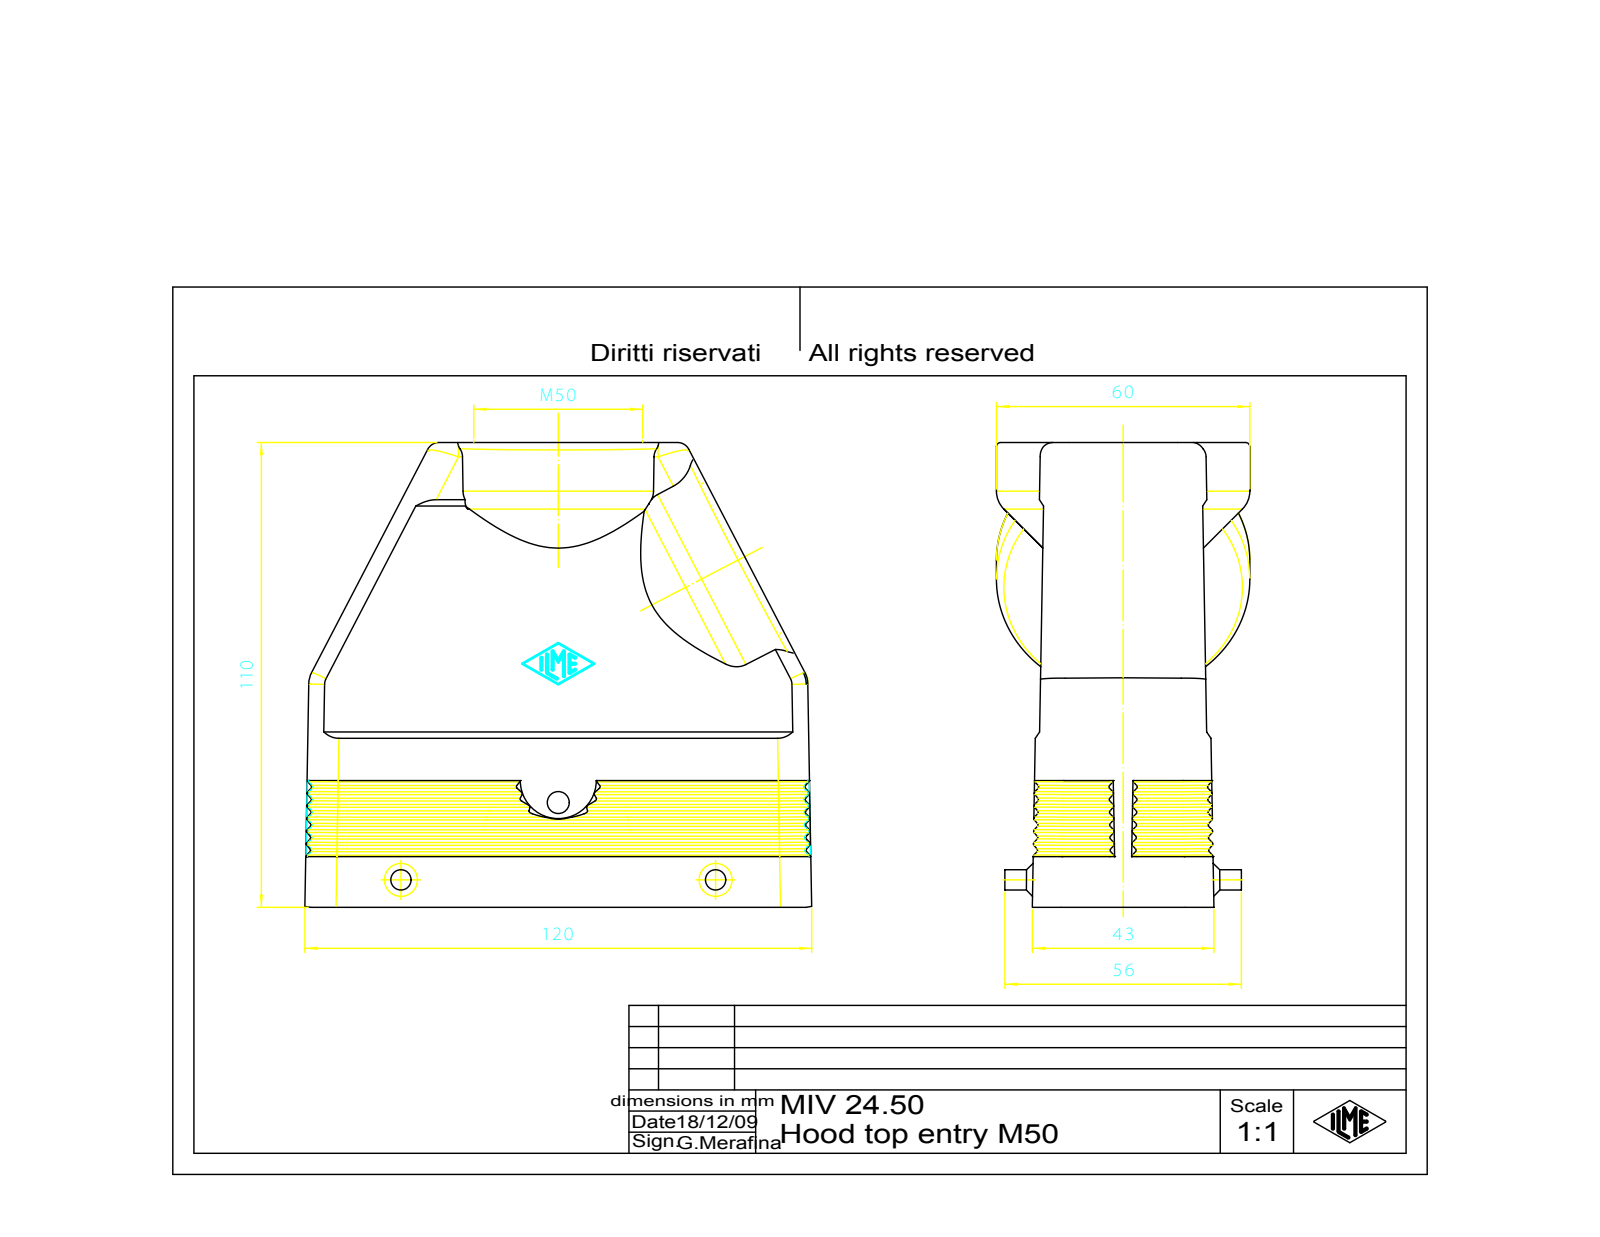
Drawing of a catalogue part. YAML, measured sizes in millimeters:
part_name: "MIV_24.50"
step_written_by: "CoCreate Modeling 16.00A 16-Aug-2008 (C) Parametric Technology GmbH (AUTOMOTIVE_DESIGN)"
units: millimeters
bodies: {solids: 1, faces: 568, planar: 204, cylindrical: 199, other: 165}
overall_size: [119.23, 109.2, 60]
volume: 106066
surface_area: 66218
round_holes:
  - {diameter: 3.5, count: 4}
  - {diameter: 5.2, count: 1}
  - {diameter: 50, count: 1}
round_bosses_or_shafts:
  - {diameter: 4.8, count: 2}
partial_cylinders:
  - {radius: 0.5, count: 78}
  - {radius: 3, count: 10}
  - {radius: 7, count: 8}
  - {radius: 4.2, count: 4}
  - {radius: 30, count: 2}
  - {radius: 33.77, count: 2}
  - {radius: 1, count: 1}
face_to_face_distances: [1.05, 2, 5.58, 2.39, 7.95, 4, 8.5, 3.99, 5.99, 7.99]
hole_center_spacings: [53.72, 27, 104, 107.45]
